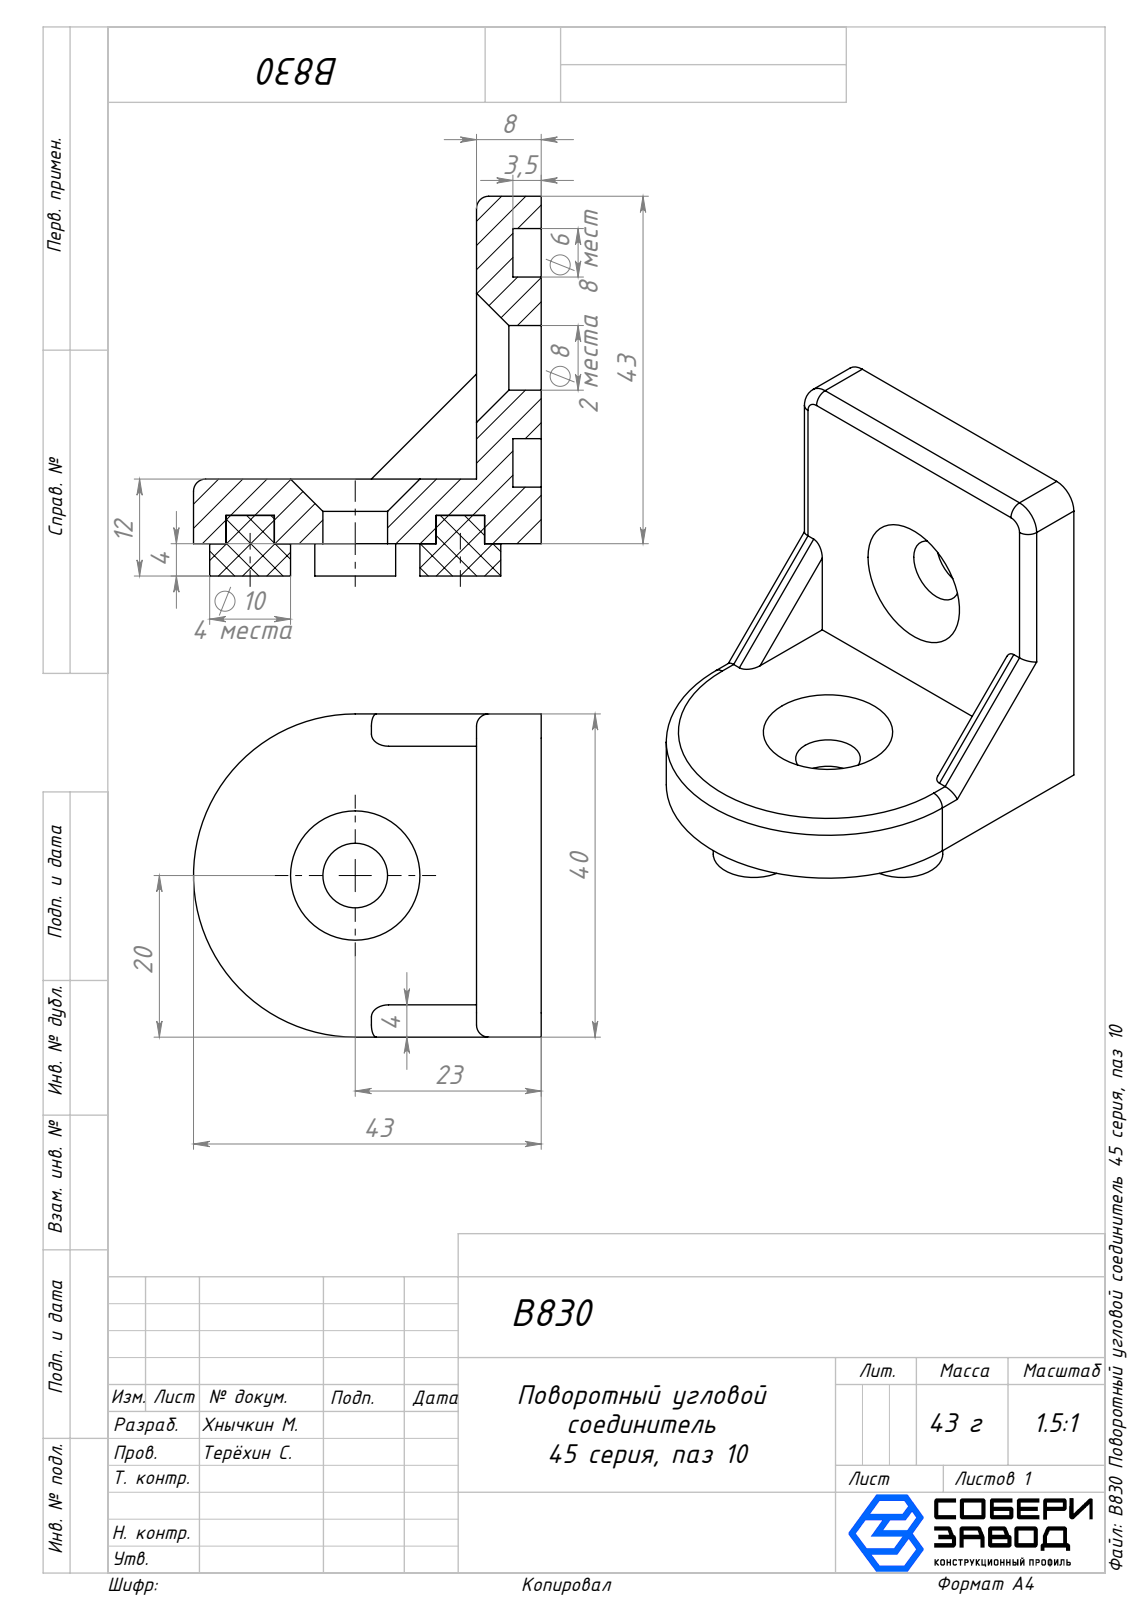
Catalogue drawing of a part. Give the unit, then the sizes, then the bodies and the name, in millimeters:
Units: millimetres
Overall size (bounding box): 47 × 43 × 40
Round holes (diameter × count): ⌀6 ×8, ⌀8 ×2
Round bosses / shafts (diameter × count): ⌀10 ×4
Partial cylindrical surfaces — rounded edges, fillets, slot ends (radius × count): R1.5 ×9, R3 ×2, R20 ×1
Main face-to-face distances: 8, 40, 4, 3.5, 4.5, 12, 7.5, 47, 43, 39.5
Hole centre spacings: 13, 18.38, 26
Volume: 23 646 mm³ · Surface area: 9 802 mm²
Bodies: 5 solids, 87 faces (31 planar, 48 cylindrical, 8 other)
Part name (STEP PRODUCT): B830 Поворотный угловой соединитель 45 серия, паз 10; Ножка_00; Корпус_00
STEP written by: SolidWorks 2025 (AUTOMOTIVE_DESIGN)
